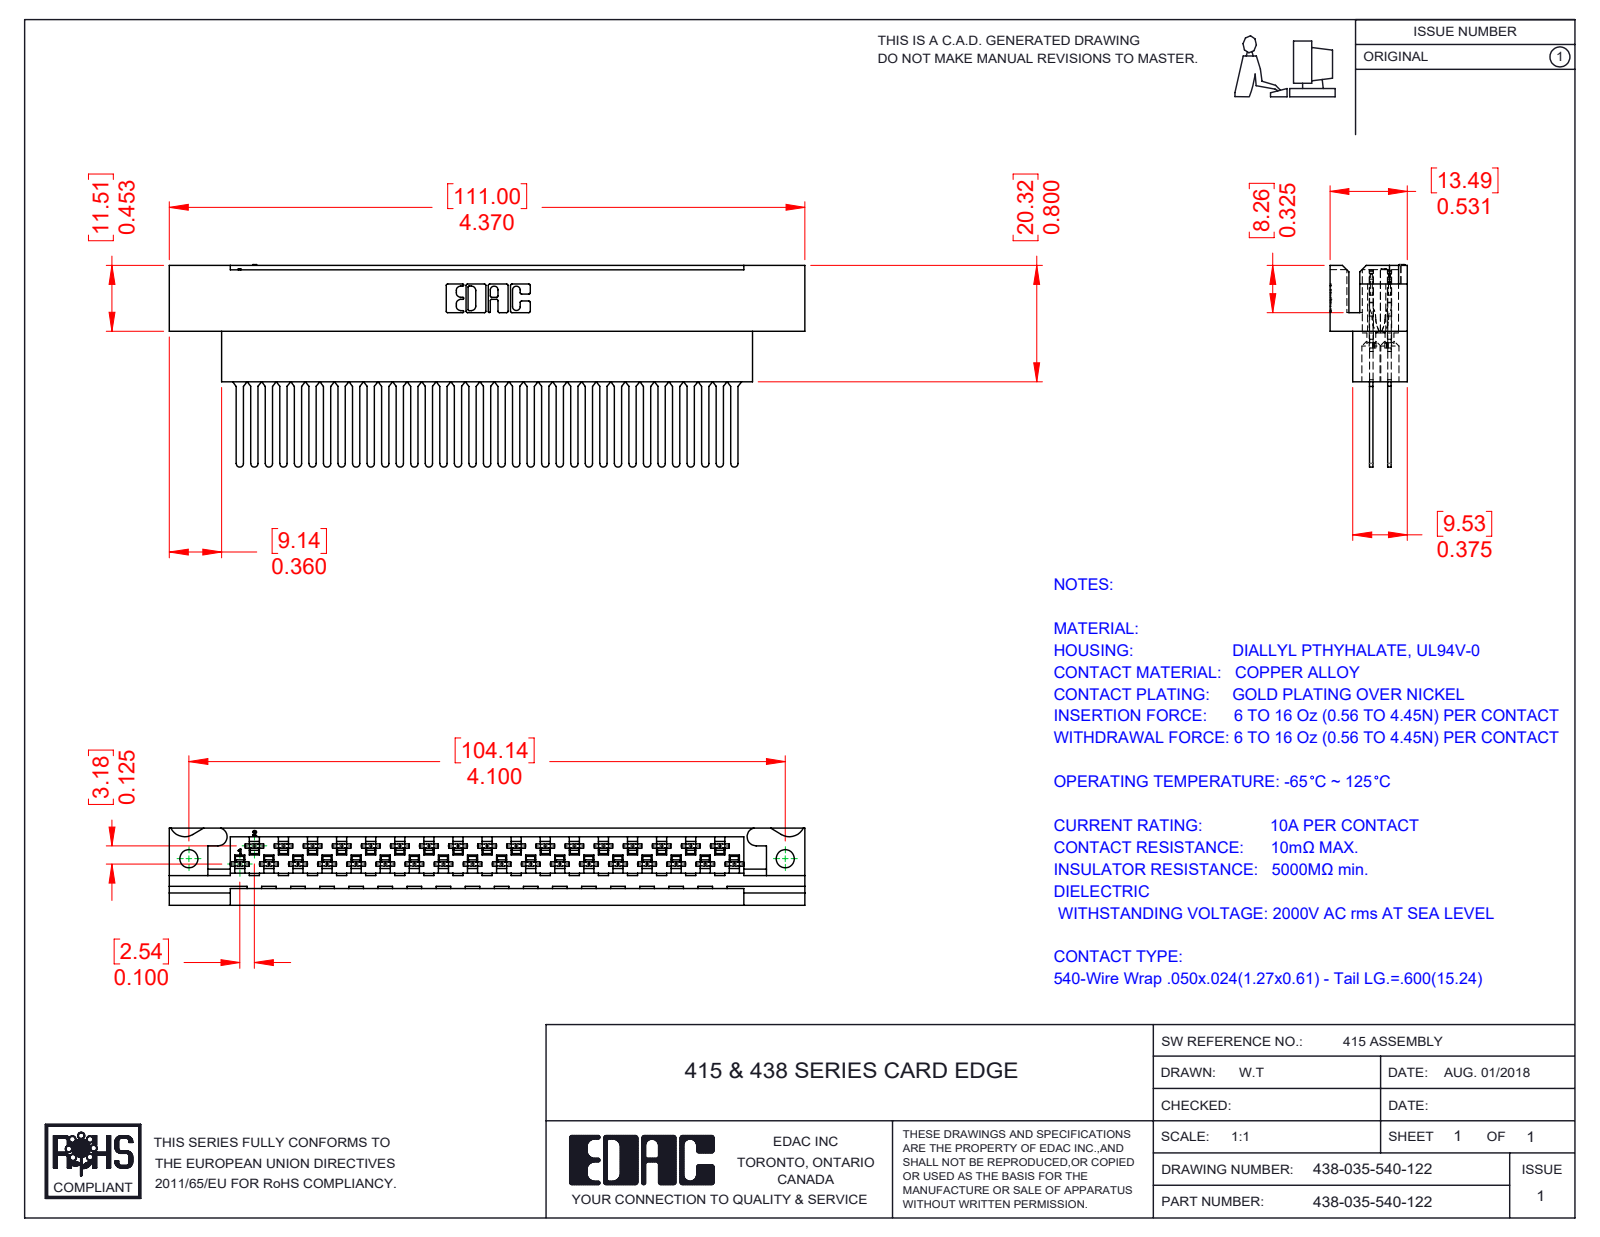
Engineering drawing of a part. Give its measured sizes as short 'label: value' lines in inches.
name: 516-290-001_540; 438-035-540-122; 438-210-001_438-210-035-112
written by: SolidWorks 2016 (CONFIG_CONTROL_DESIGN)
unit: in
bodies: 36 solids, 3586 faces (2289 planar, 960 cylindrical, 337 other)
size: 4.37 × 1.391 × 0.531
volume: 1.127 in³; area: 37.18 in²
holes: 35× ⌀0.05, 35× ⌀0.13, 1× ⌀0.125, 1× ⌀0.125
rounds: 140× R0.012, 140× R0.022, 70× R0.007, 70× R0.008, 70× R0.016, 70× R0.08, 35× R0.025, 22× R0.01
face distances: 0.125, 0.024, 0.074, 0.05, 0.295, 0.531, 0.115, 0.156, 0.26, 0.271
hole spacings: 0.2, 0.4, 0.6, 0.8, 1, 1.2, 1.4, 0.1
